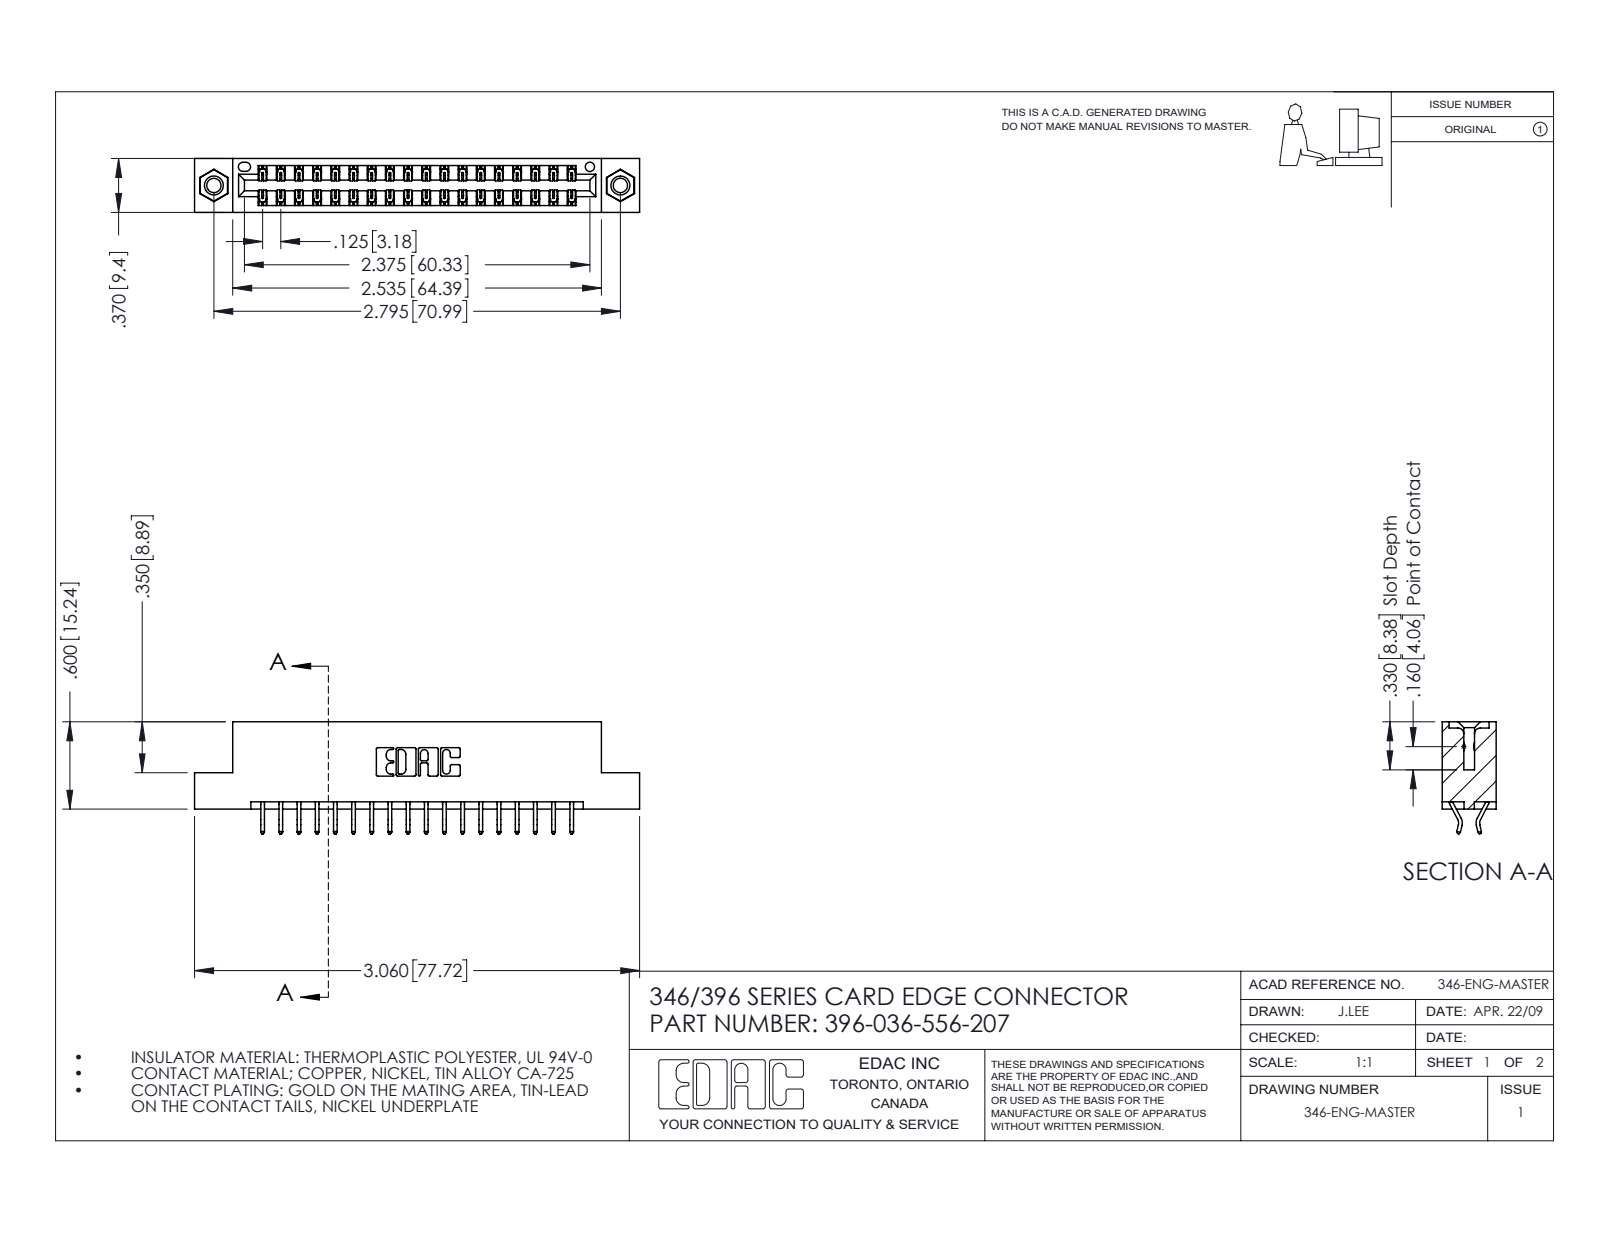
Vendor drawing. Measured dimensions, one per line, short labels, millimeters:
name: 346 Part_Flush Mounting Lugs - 0.156 Dia-TI; 345-250-001_345-250-005-103; 345-292-001_556 Tail; 396-036-556-207
written by: SolidWorks 2016 (CONFIG_CONTROL_DESIGN)
unit: mm
bodies: 39 solids, 2270 faces (1512 planar, 742 cylindrical, 16 other)
size: 77.7 × 19.6 × 9.4
volume: 7 370 mm³; area: 9 761 mm²
holes: 2× ⌀2.5, 2× ⌀3.2, 2× ⌀4, 1× ⌀1.6
bosses: 2× ⌀3.9
rounds: 54× R0.2, 22× R0.3, 6× R0.2, 6× R0.8, 3× R0.7, 2× R0.3, 2× R0.4, 2× R0.6
face distances: 1.2, 8.2, 6.4, 9.4, 0.6, 1.8, 7.6, 7, 3.8, 5.6
hole spacings: 6.2, 65.7, 71
